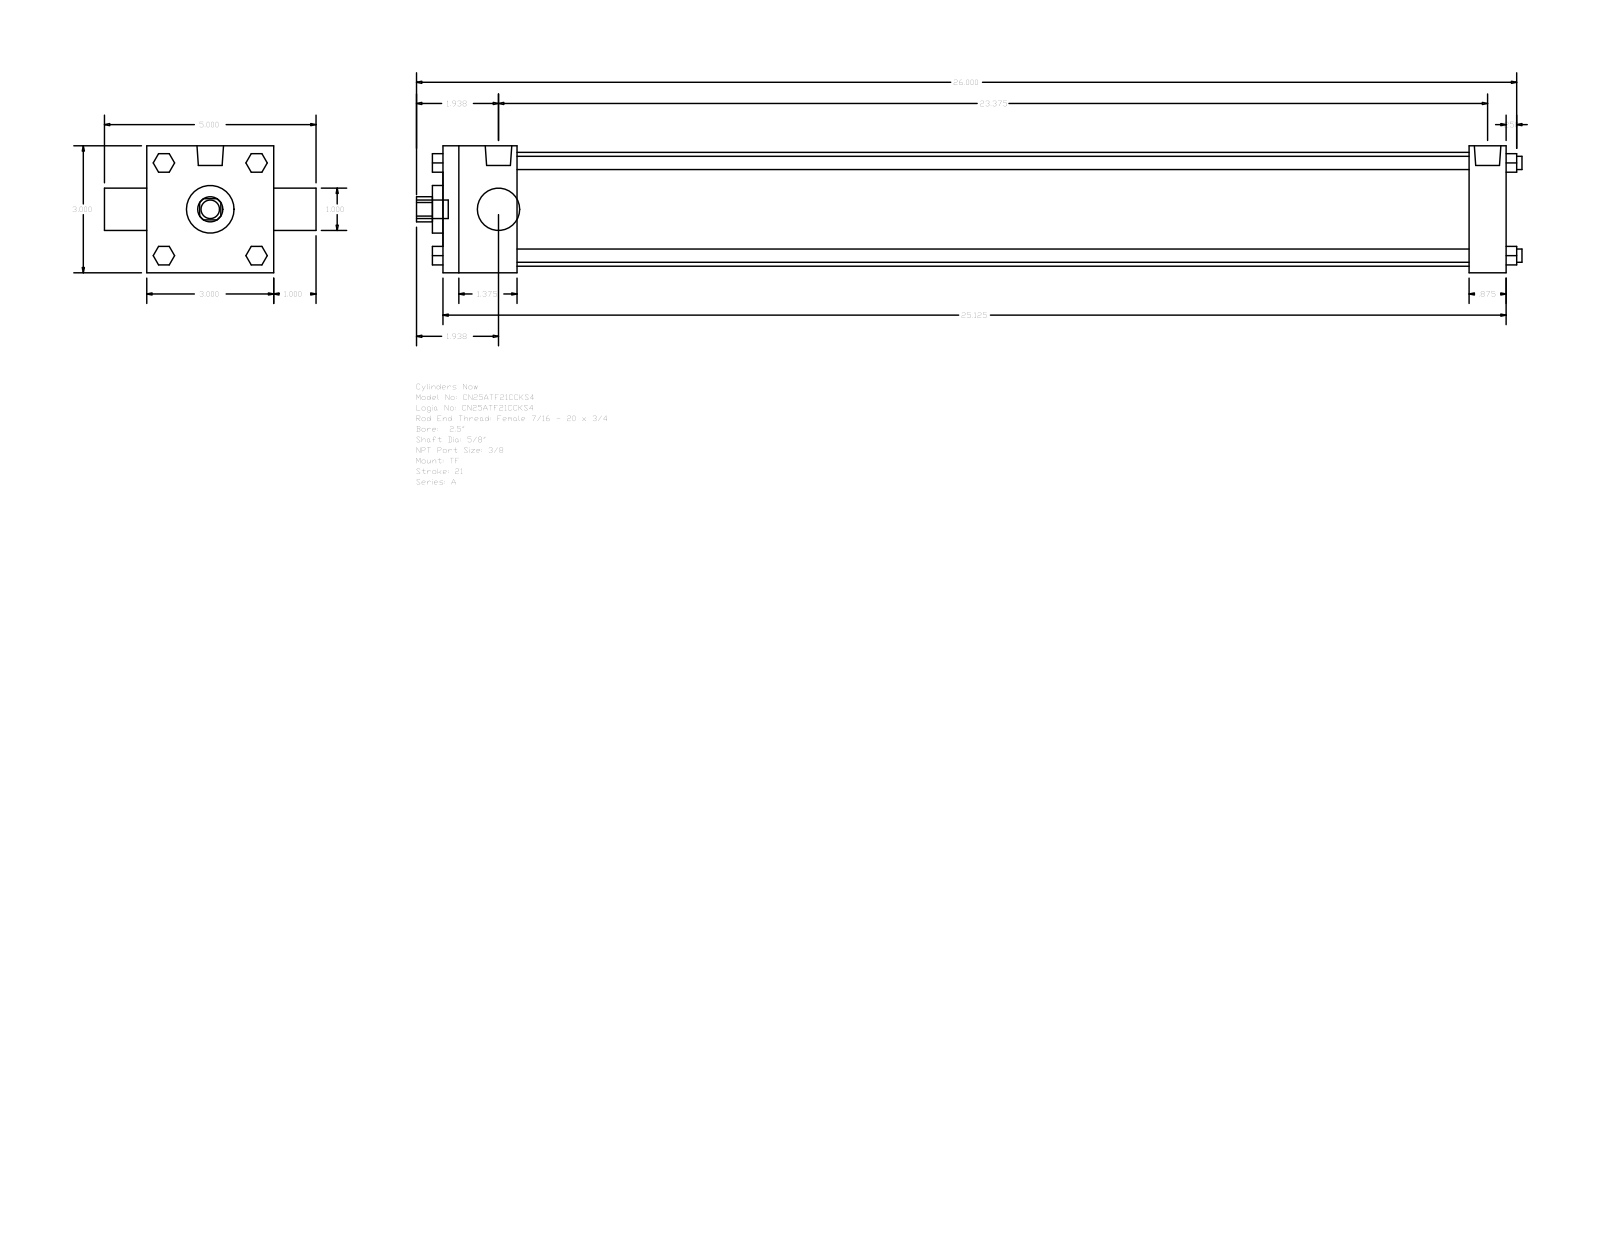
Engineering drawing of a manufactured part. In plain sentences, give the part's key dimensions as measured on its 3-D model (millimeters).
The part is named "A_TF__0250_0.625". Its 3-D file was written by "GSSL Pune (CONFIG_CONTROL_DESIGN)". It is 0 solids with 120 faces: 92 planar, 28 cylindrical and 0 other. Overall it measures 663.58 by 127 by 76.2 millimeters. Round holes: 1 of diameter 15.88, 1 of diameter 25.4, 1 of diameter 28.57, 1 of diameter 68.33. Round bosses or shafts: 4 of diameter 7.94, 3 of diameter 5.56, 2 of diameter 15.93, 1 of diameter 11.11. Partial cylindrical surfaces (rounded edges, fillets, slot ends): 1 of radius 7.54. The main face-to-face distances are 76.2, 638.17, 44.45, 615.95, 571.5, 593.72, 22.22, 25.4, 101.6, 6.35.
